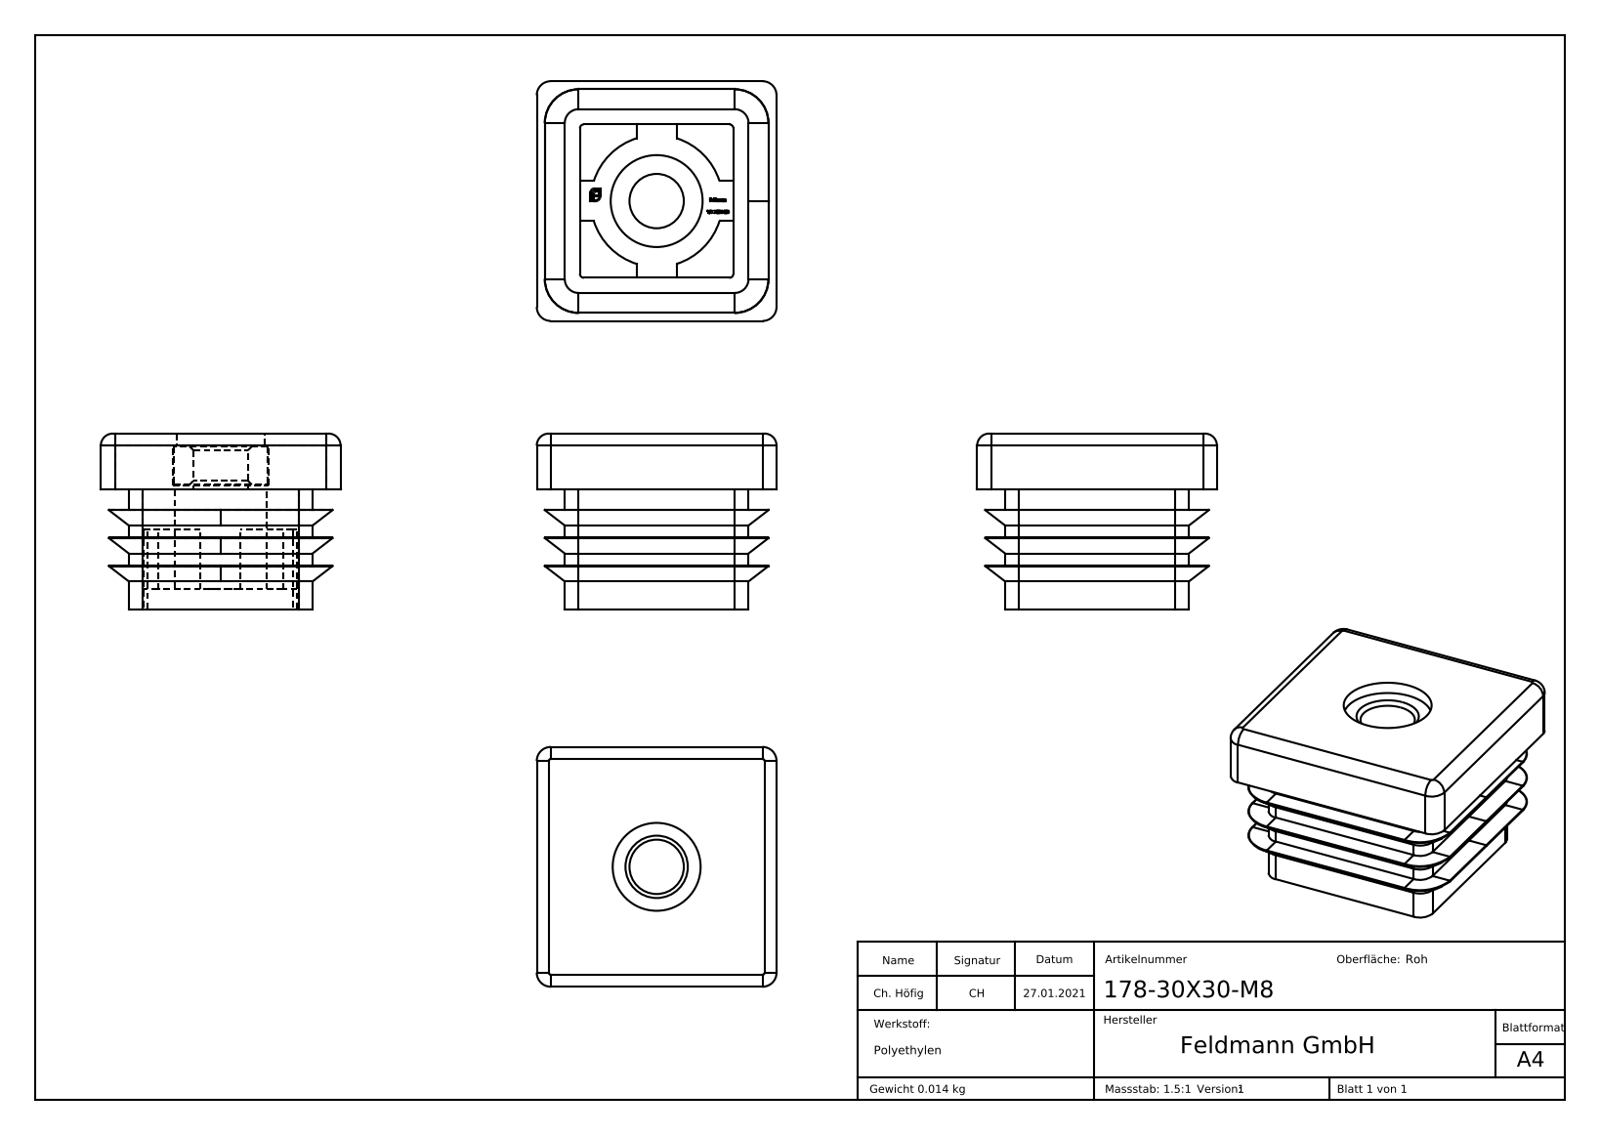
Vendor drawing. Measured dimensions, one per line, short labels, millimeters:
name: 178-30X30-M8
written by: SolidWorks 2018 (CONFIG_CONTROL_DESIGN)
unit: mm
bodies: 2 solids, 500 faces (250 planar, 70 cylindrical, 180 other)
size: 30 × 30 × 22
volume: 11 306 mm³; area: 7 254 mm²
holes: 1× ⌀6.8, 1× ⌀11, 1× ⌀11.5
rounds: 8× R1.75, 4× R0.5, 4× R1.5, 1× R8.25
face distances: 3.5, 7, 5.4, 26.5, 24.6, 1.9, 21.1, 5.5, 9, 2.5
